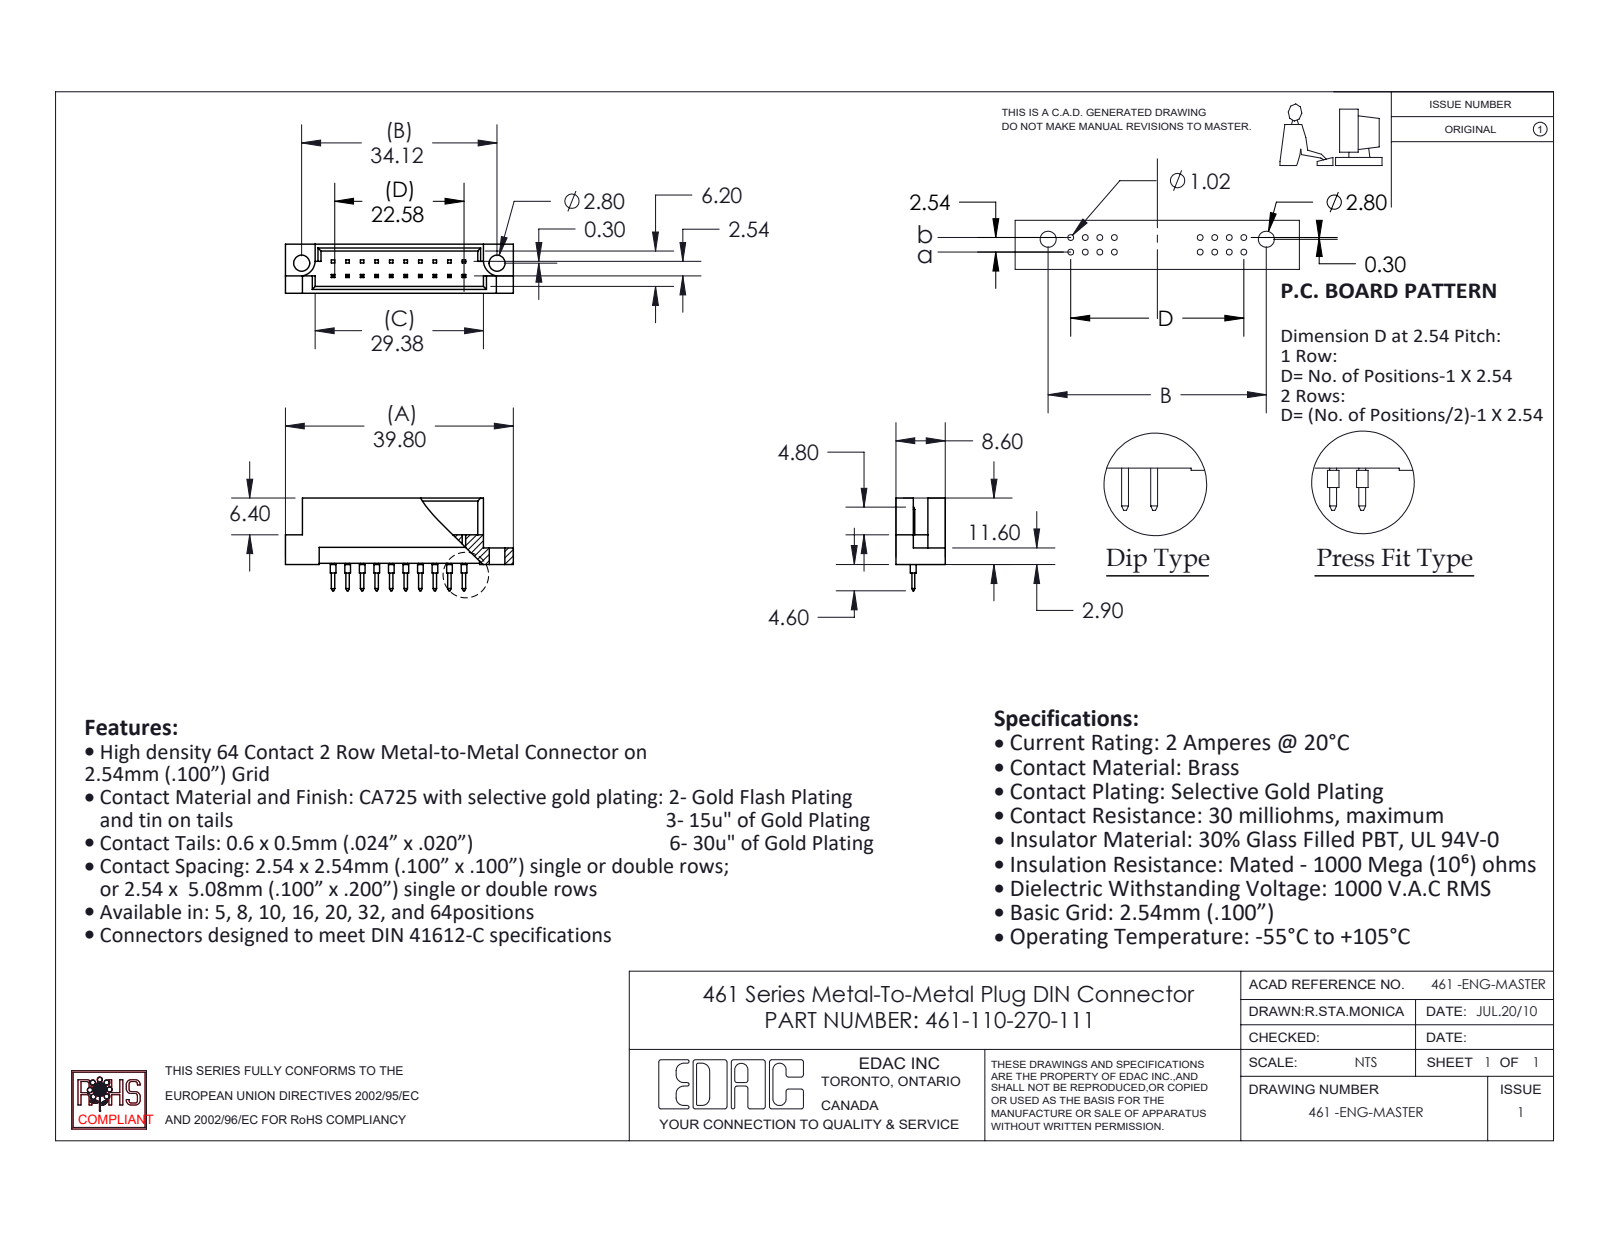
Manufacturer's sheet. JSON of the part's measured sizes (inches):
{"part_name": "461-110-270-111; 461-290_70; 461 Part_20", "step_written_by": "SolidWorks 2020 (CONFIG_CONTROL_DESIGN)", "units": "inches", "bodies": {"solids": 11, "faces": 348, "planar": 322, "cylindrical": 26, "other": 0}, "overall_size": [1.567, 0.638, 0.339], "volume_in3": 0.119, "surface_area_in2": 4.152, "round_holes": [[0.11, 2]], "round_bosses_or_shafts": [[0.039, 10]], "partial_cylinders_radius": [[0.11, 2]], "face_to_face_distances": [0.047, 0.291, 0.339, 0.244, 0.1, 0.197, 0.062, 0.109, 0.129, 0.209], "hole_center_spacings": [1.343]}
